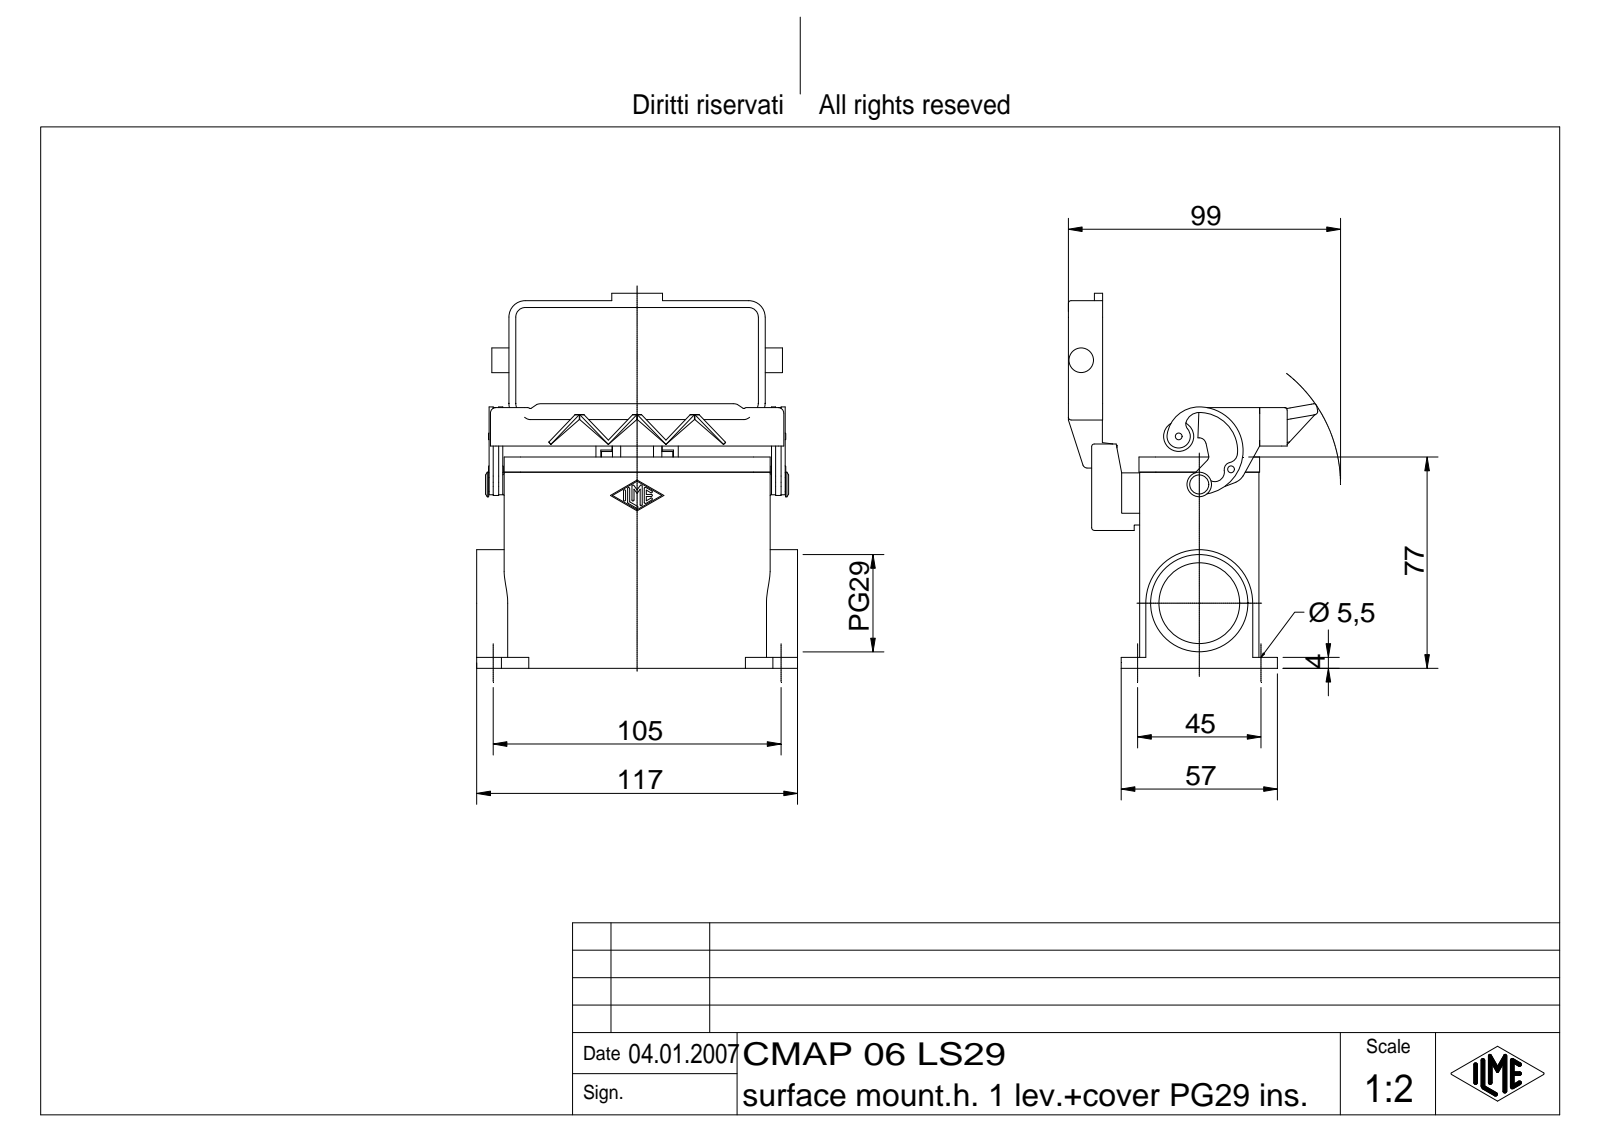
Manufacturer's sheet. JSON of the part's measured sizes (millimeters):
{"part_name": "CMAP 06 LS29", "step_written_by": "Autodesk Inventor 7 (AUTOMOTIVE_DESIGN)", "units": "millimeters", "bodies": {"solids": 6, "faces": 609, "planar": 265, "cylindrical": 180, "other": 164}, "overall_size": [136.7, 117, 90.95], "volume_mm3": 156636, "surface_area_mm2": 86850, "round_holes": [[5.5, 4], [2, 1], [4, 1], [29.48, 1], [35.48, 1]], "round_bosses_or_shafts": [[9, 2], [5, 2], [11, 1], [7, 1], [4, 1], [3, 1], [2.5, 1]], "partial_cylinders_radius": [[1, 18], [0.38, 14], [2, 12], [6, 12], [1.5, 6], [3.5, 6], [3, 4], [0.5, 3]], "face_to_face_distances": [3, 40.5, 43.5, 4, 37.5, 26, 66.5, 22.5, 69.5, 29], "hole_center_spacings": [45, 105, 114.24, 50.12]}
